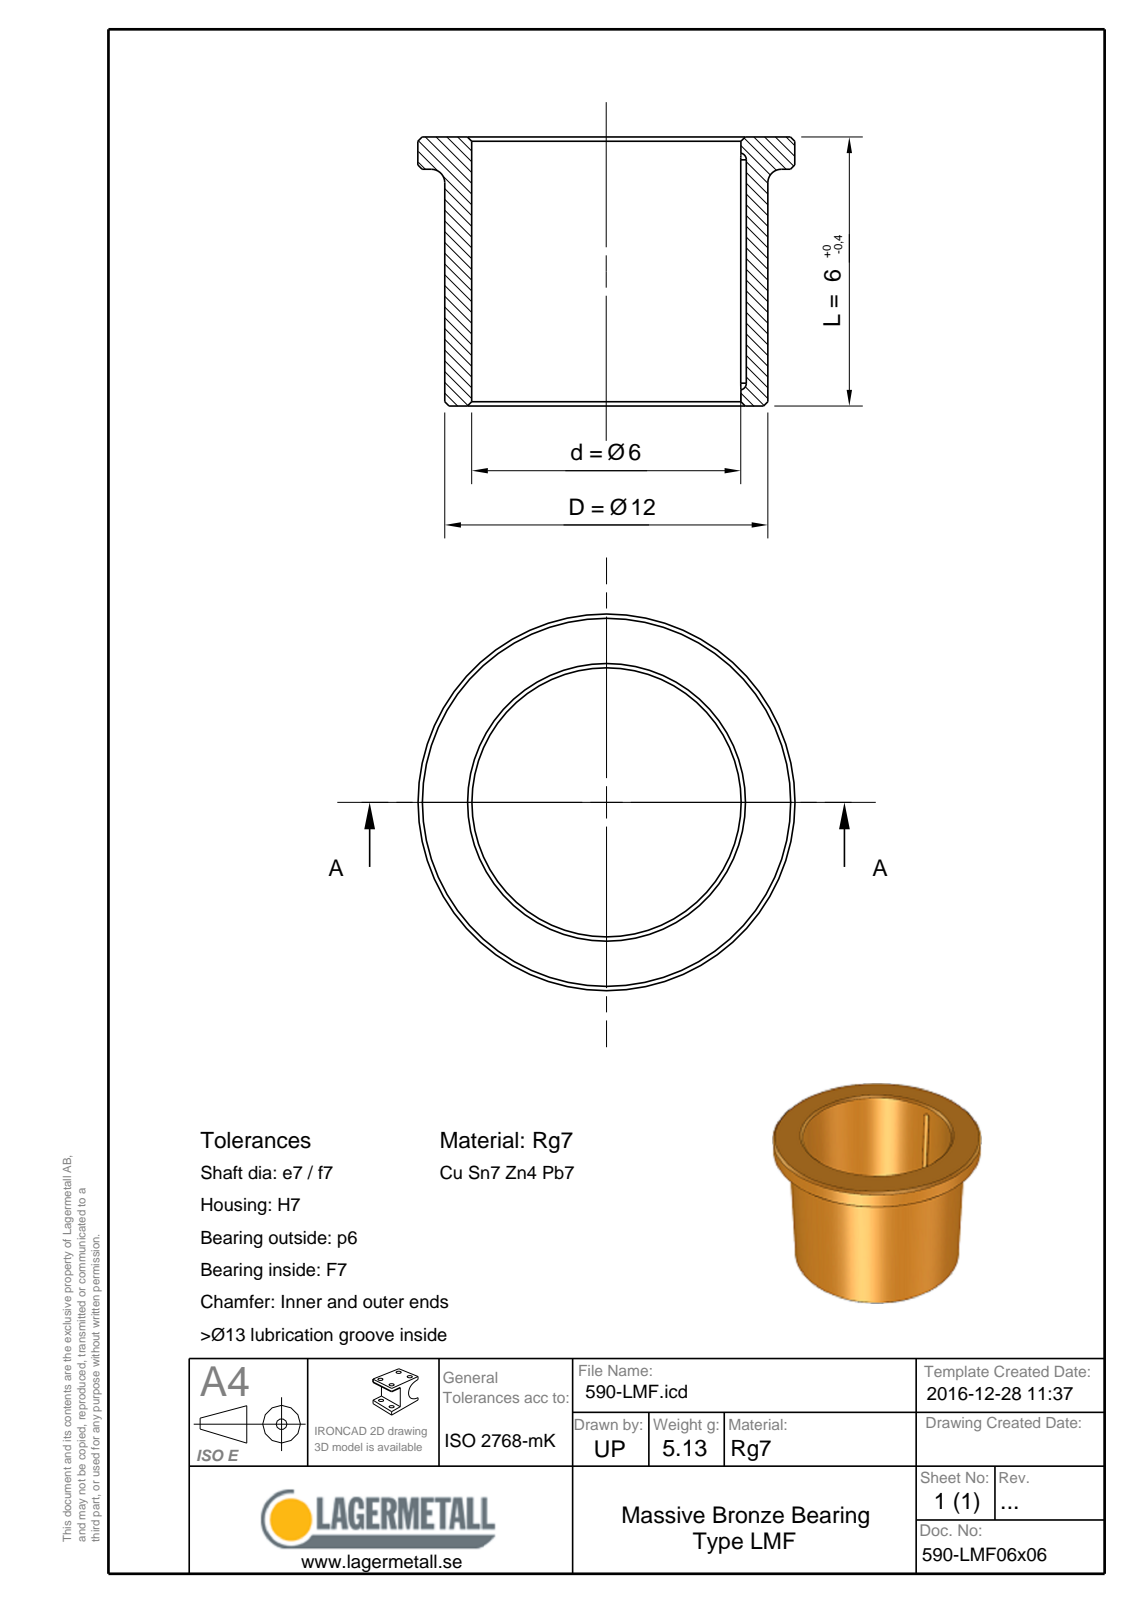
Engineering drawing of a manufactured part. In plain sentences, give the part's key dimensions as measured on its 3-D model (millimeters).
The part is named "590-LMF06x06". Its 3-D file was written by "Spatial InterOp 3D (CONFIG_CONTROL_DESIGN)". It is 1 solid with 11 faces: 3 planar, 3 cylindrical and 5 other. Overall it measures 14 by 14 by 6 millimeters. Its volume is 583 cubic millimeters and its surface area 574 square millimeters. Round holes: 1 of diameter 6. Round bosses or shafts: 1 of diameter 14, 1 of diameter 12. The main face-to-face distances are 6, 4, 2.
